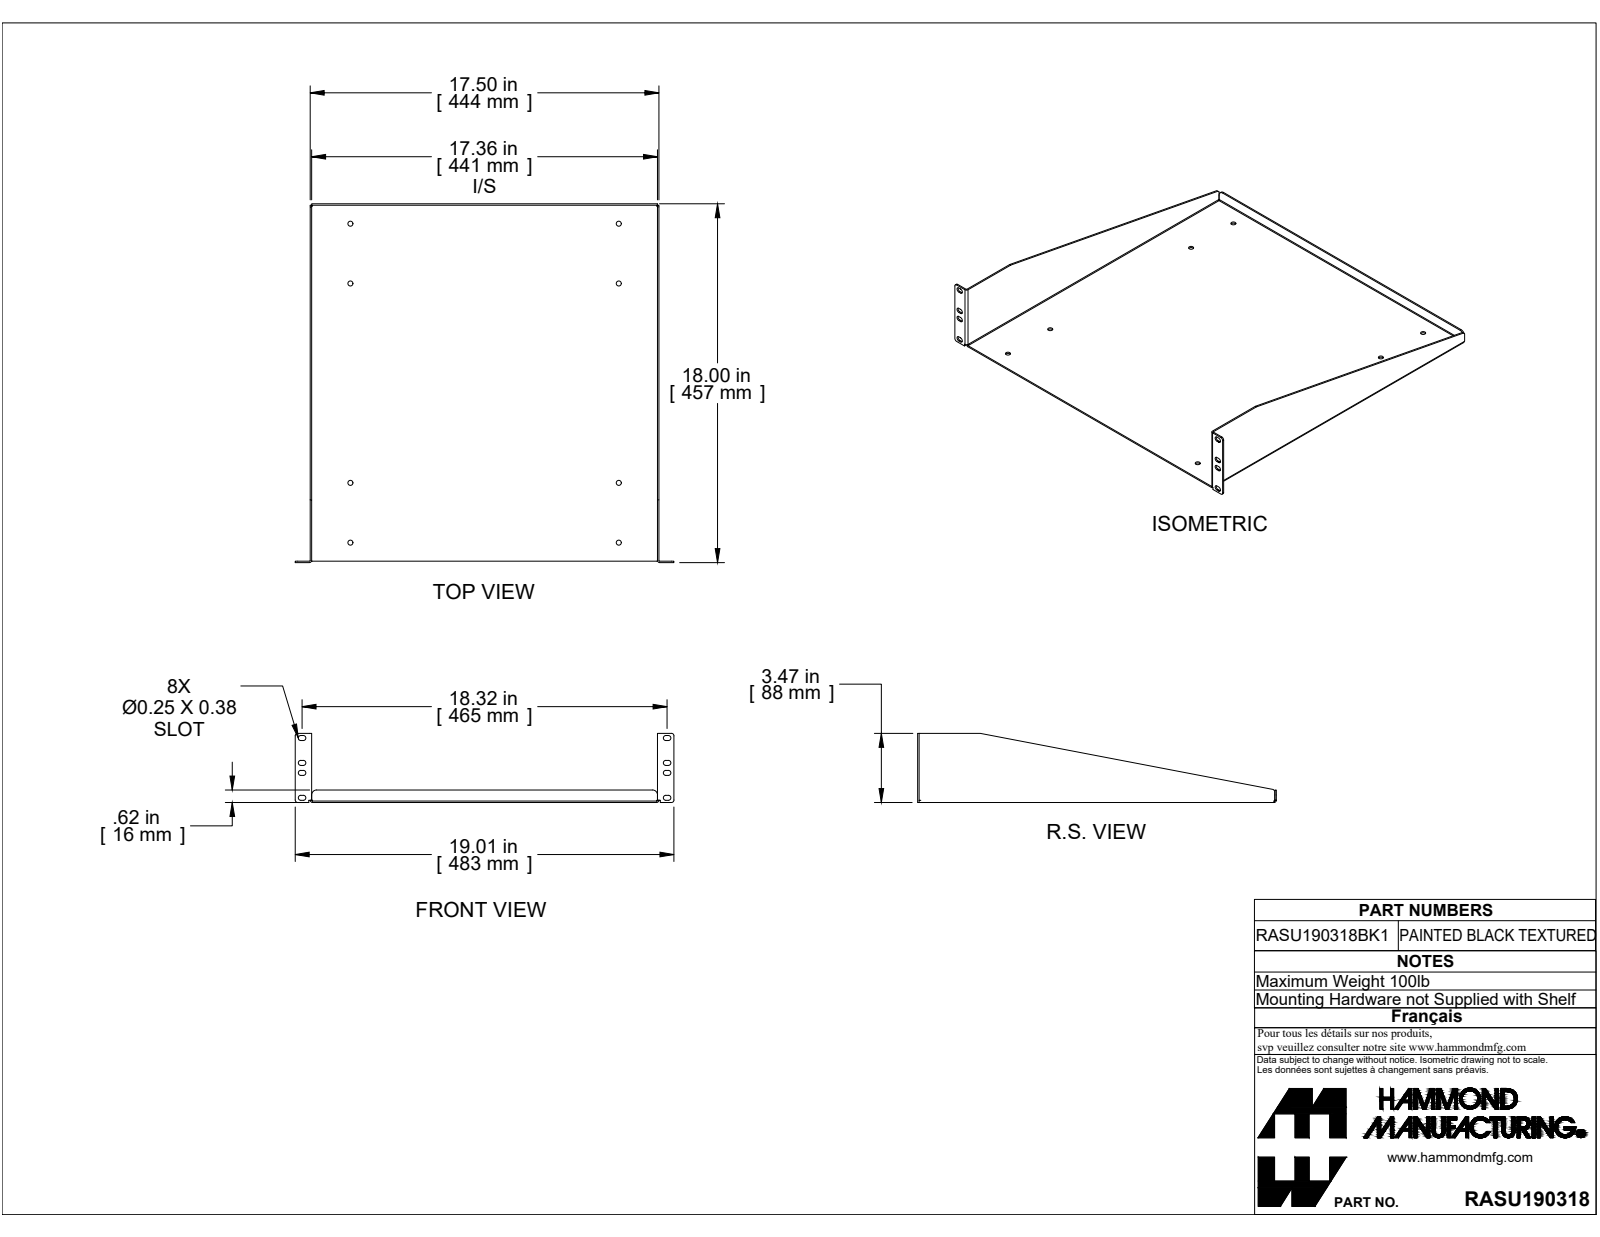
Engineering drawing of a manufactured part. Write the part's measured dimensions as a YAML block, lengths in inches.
part_name: "RASU190318BK1"
step_written_by: "SolidWorks 2019 (CONFIG_CONTROL_DESIGN)"
units: inches
bodies: {solids: 1, faces: 104, planar: 56, cylindrical: 44, other: 4}
overall_size: [19.006, 18, 3.468]
volume: 29.2
surface_area: 818.1
round_holes:
  - {diameter: 0.25, count: 8}
partial_cylinders:
  - {radius: 0.125, count: 20}
  - {radius: 0.036, count: 5}
  - {radius: 0.108, count: 5}
  - {radius: 0.055, count: 3}
  - {radius: 0.25, count: 2}
face_to_face_distances: [0.072, 17.428, 17.356, 17.5, 17.856, 17.928, 0.072, 17.928, 18, 0.625]
hole_center_spacings: [3, 13, 13.468, 13.798, 18.719, 10, 16, 16.774]
